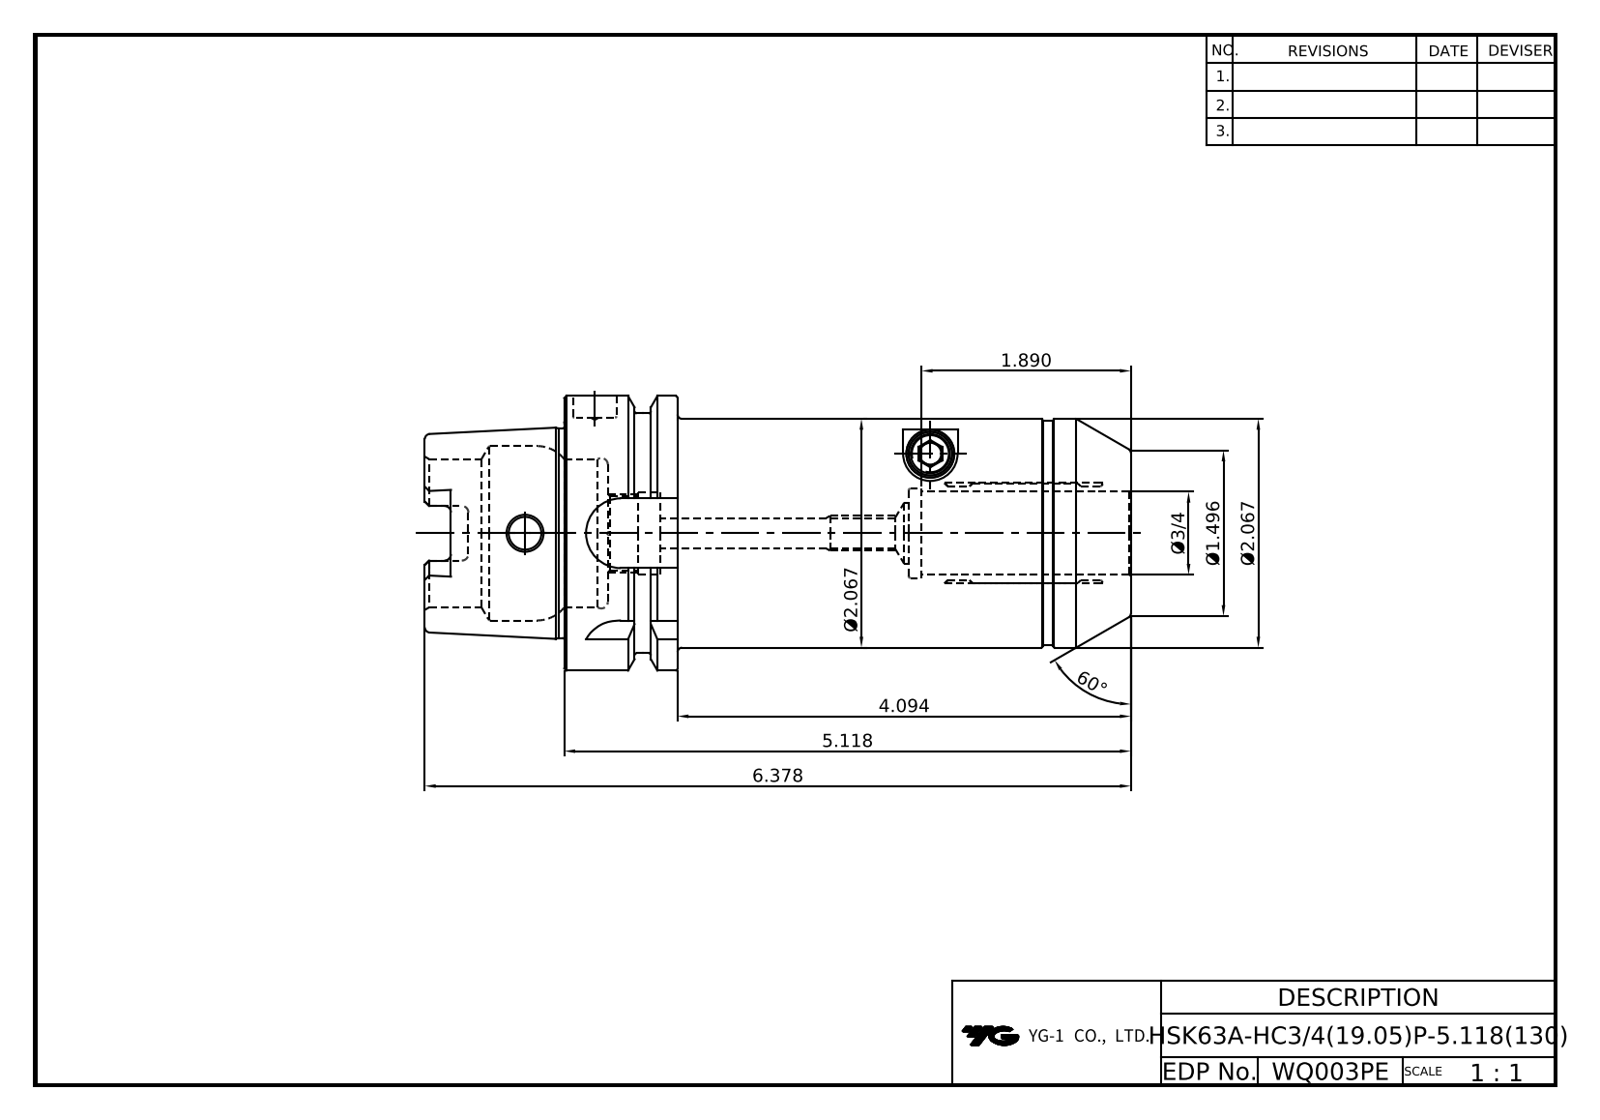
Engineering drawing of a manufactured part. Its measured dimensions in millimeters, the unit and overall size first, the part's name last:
Units: millimetres
Overall size (bounding box): 162 × 63 × 63
Round holes (diameter × count): ⌀6.92 ×1, ⌀7.5 ×1, ⌀10 ×1, ⌀14 ×1, ⌀16.92 ×1, ⌀19 ×1, ⌀19.05 ×1, ⌀19.85 ×1, ⌀34 ×1, ⌀40 ×1
Round bosses / shafts (diameter × count): ⌀63 ×1, ⌀55 ×1, ⌀52.5 ×1, ⌀51.5 ×1, ⌀48.04 ×1
Partial cylindrical surfaces — rounded edges, fillets, slot ends (radius × count): R1.5 ×6, R2.88 ×4, R8 ×4
Main face-to-face distances: 130, 104, 10, 26, 16, 120, 32, 52, 42, 58
Volume: 282 593 mm³ · Surface area: 42 686 mm²
Bodies: 1 solid, 126 faces (43 planar, 36 cylindrical, 47 other)
Part name (STEP PRODUCT): LO-HSK63A-HC19.05P-130
STEP written by: Autodesk Inventor 2022 (AUTOMOTIVE_DESIGN)
